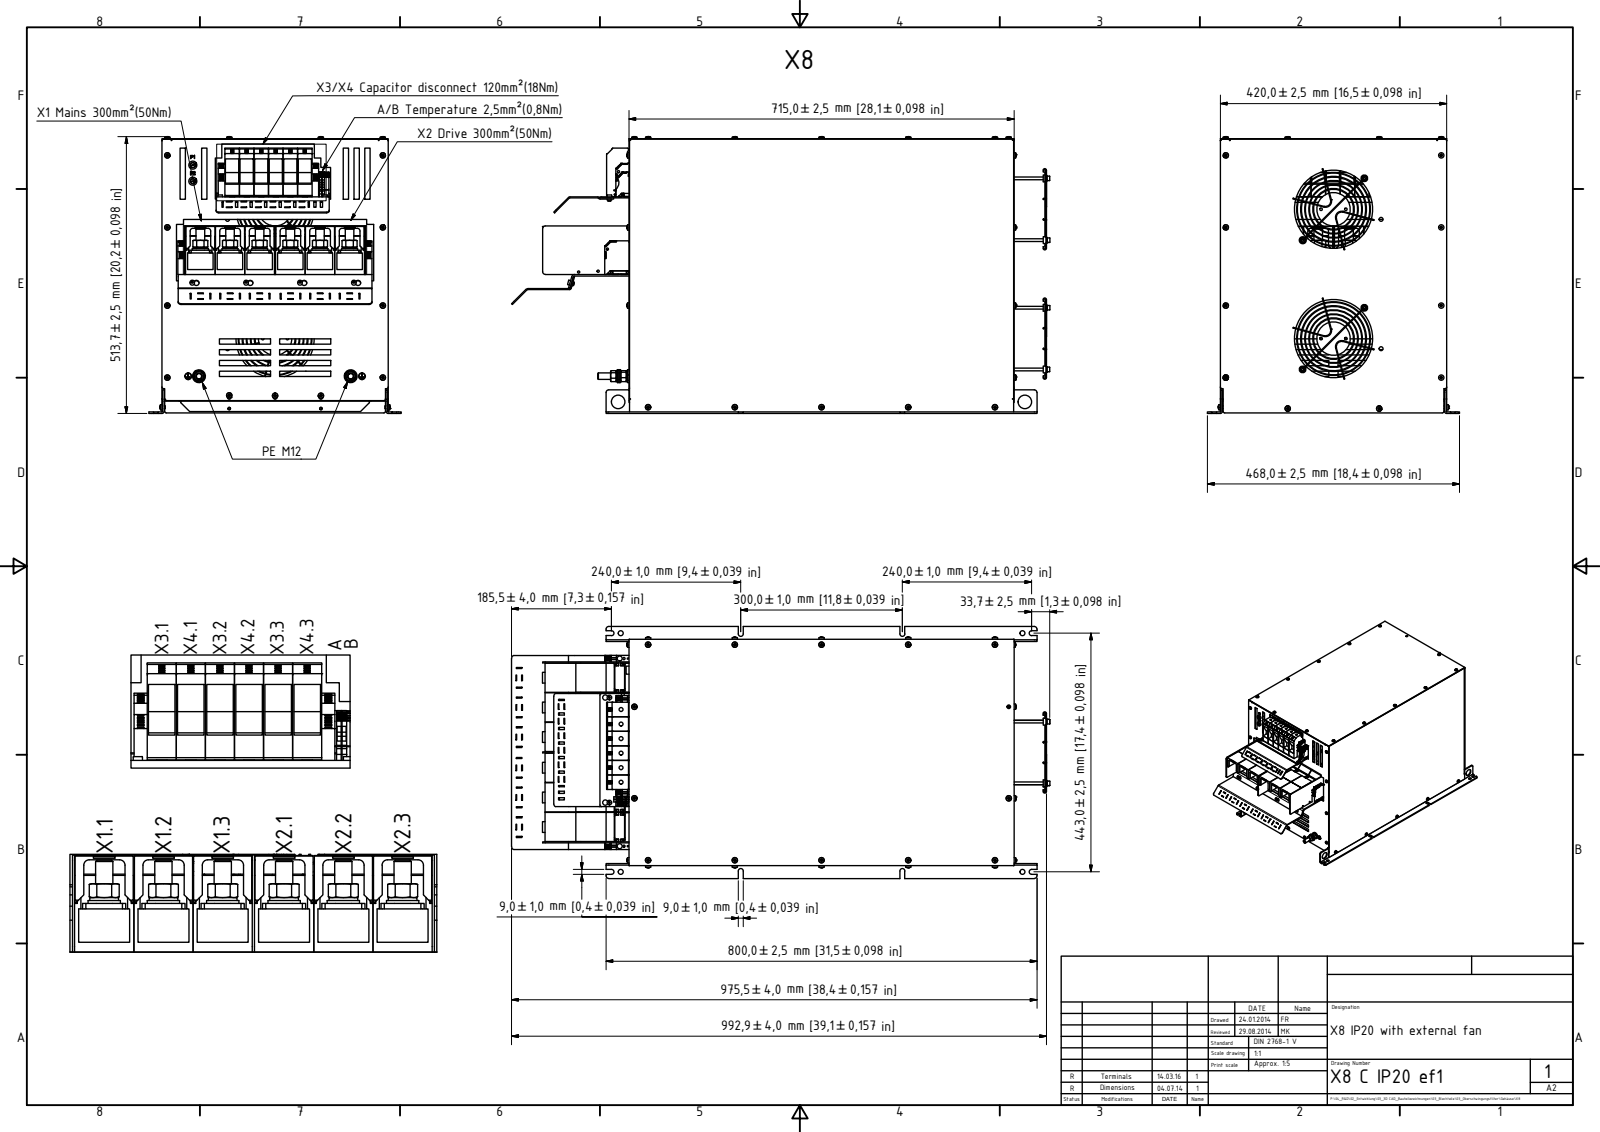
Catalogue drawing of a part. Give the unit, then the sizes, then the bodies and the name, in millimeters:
Units: millimetres
Overall size (bounding box): 978.91 × 513.88 × 468
Round holes (diameter × count): ⌀4.13 ×36, ⌀6.5 ×33, ⌀7 ×28, ⌀3.24 ×20, ⌀5 ×10, ⌀6 ×10, ⌀4 ×9, ⌀10 ×6, ⌀3.95 ×4, ⌀4.25 ×4, ⌀5.3 ×4, ⌀5.4 ×4
Round bosses / shafts (diameter × count): ⌀5 ×36, ⌀4.6 ×32, ⌀1.4 ×16, ⌀16 ×14, ⌀8.5 ×14, ⌀30 ×12, ⌀26.7 ×12, ⌀9.2 ×6
Partial cylindrical surfaces — rounded edges, fillets, slot ends (radius × count): R0.83 ×184, R1 ×134, R0.15 ×113, R0.5 ×71, R0.31 ×64, R0.1 ×61, R2 ×61, R3.25 ×54
Main face-to-face distances: 1, 419, 418, 420, 3, 714, 2, 483, 484, 486
Hole centre spacings: 100, 21, 161, 7.5, 200, 322, 400, 27
Volume: 6 646 000 mm³ · Surface area: 5 422 000 mm²
Bodies: 153 solids, 10483 faces (6546 planar, 2330 cylindrical, 1607 other)
Part name (STEP PRODUCT): 10100531 Seitenwand X8-A1; 10100530 Lüfterblech X8-A1; 10100529 Anschlussblech X8-A1; DIN 7985 (Z) - M5x6-Z (+8 more)
STEP written by: Autodesk Inventor 2015 (AUTOMOTIVE_DESIGN)
